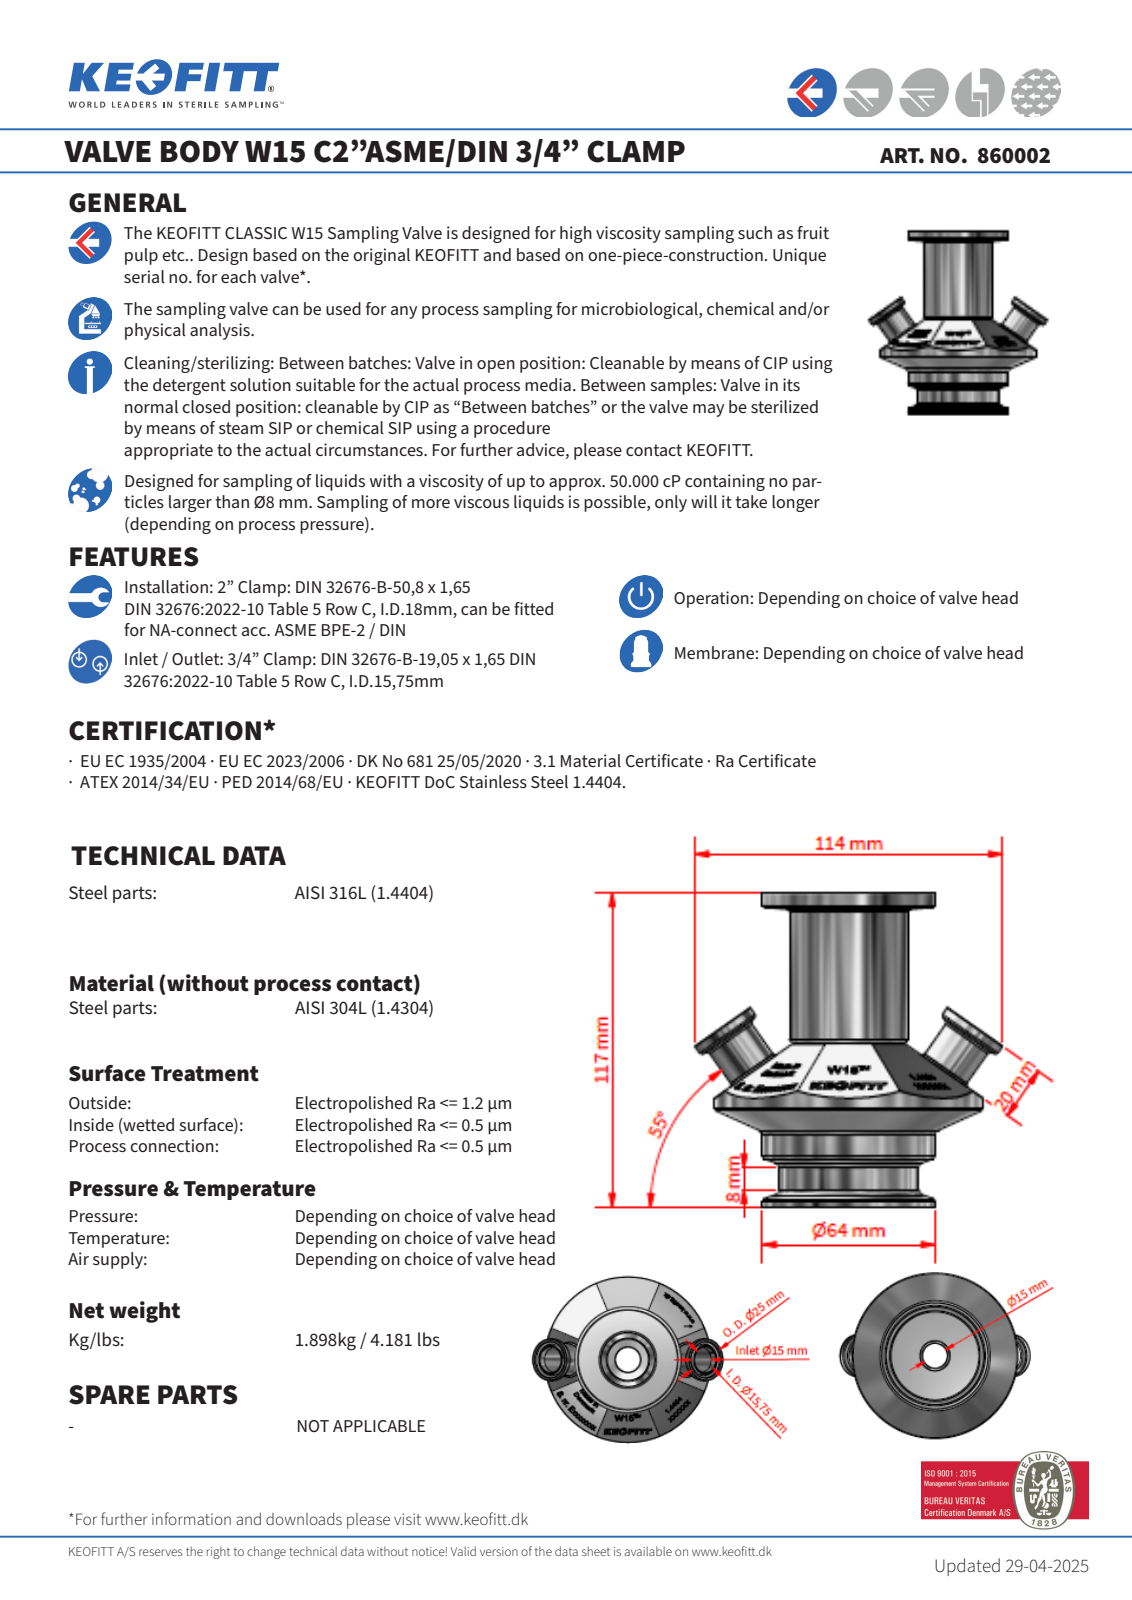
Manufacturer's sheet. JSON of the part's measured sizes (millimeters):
{"part_name": "860002; 860002_Simplify_1", "step_written_by": "Autodesk Inventor 2022 (AUTOMOTIVE_DESIGN)", "units": "millimeters", "bodies": {"solids": 1, "faces": 62, "planar": 16, "cylindrical": 12, "other": 34}, "overall_size": [116.7, 114.03, 99.5], "volume_mm3": 347381, "surface_area_mm2": 40886, "round_holes": [[21.8, 2]], "round_bosses_or_shafts": [[25, 2], [19, 2], [99.5, 1], [64, 1], [52, 1], [44, 1]], "face_to_face_distances": [116.7, 19.2, 20, 0.8, 60.6, 56.1]}
